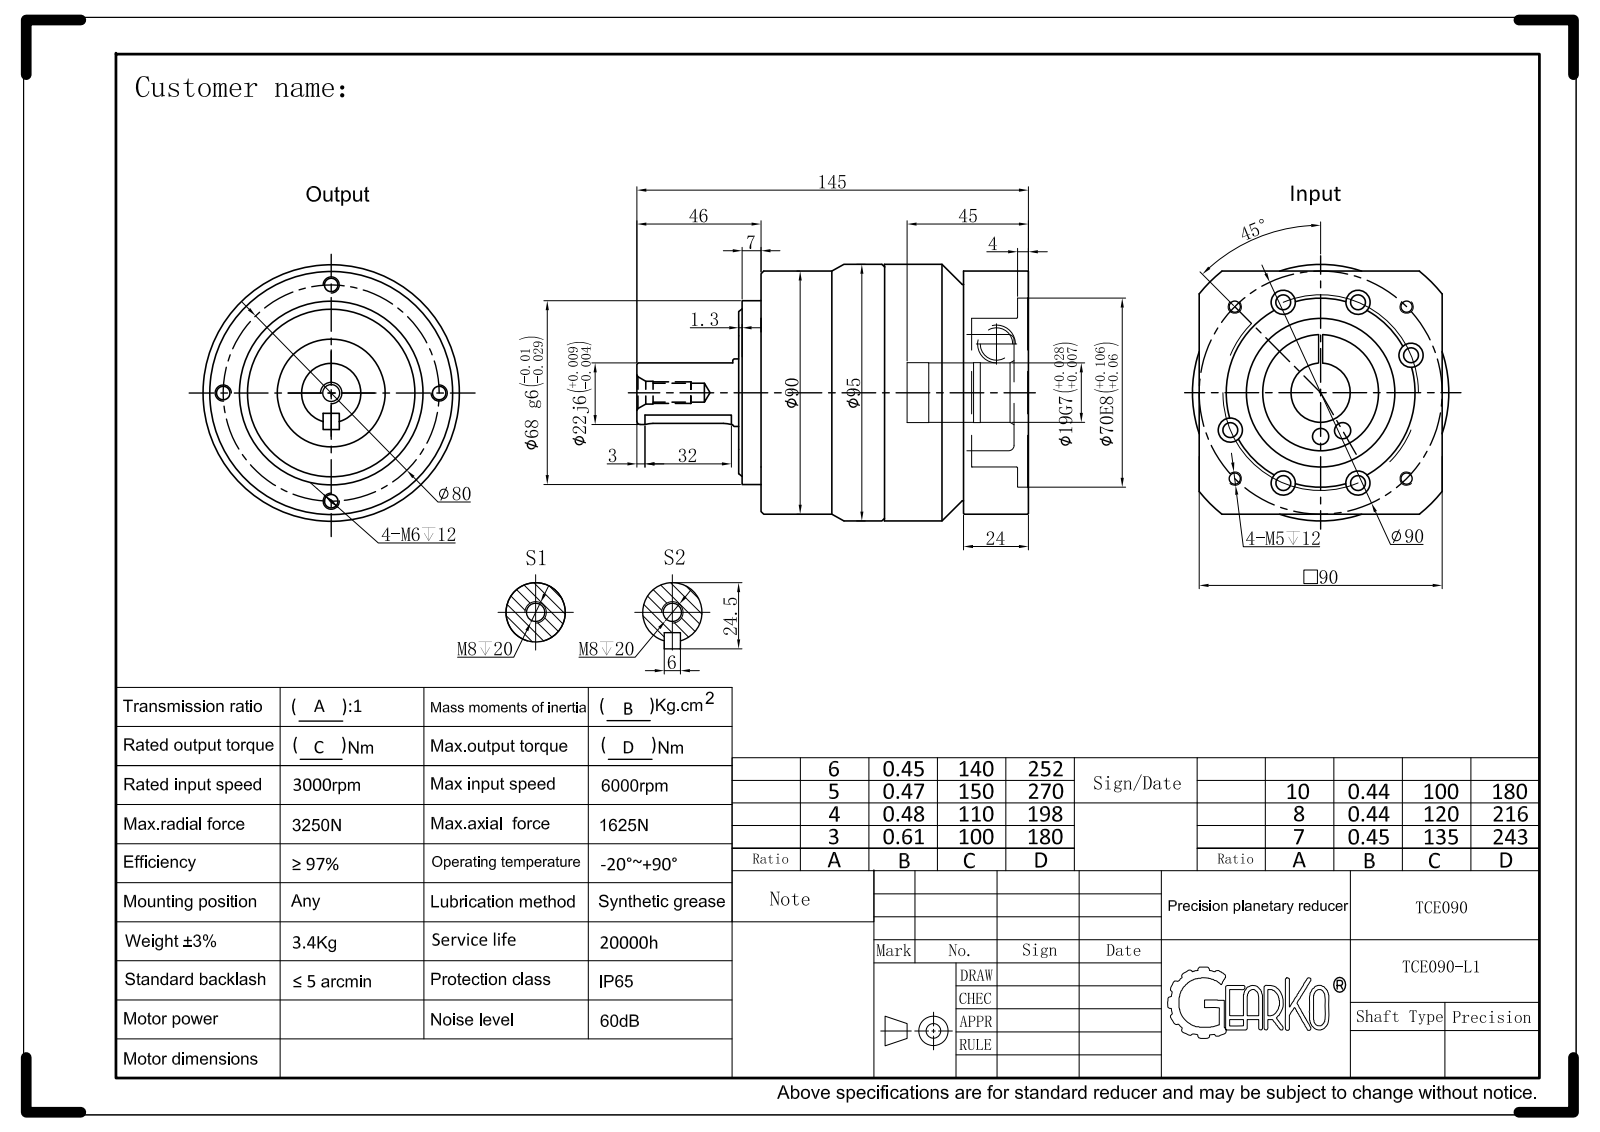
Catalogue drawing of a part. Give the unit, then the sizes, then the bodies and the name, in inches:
Units: inches
Overall size (bounding box): 5.709 × 3.74 × 3.74
Round holes (diameter × count): ⌀0.165 ×4, ⌀0.201 ×4, ⌀0.236 ×2, ⌀0.256 ×1, ⌀0.276 ×1, ⌀0.394 ×1, ⌀0.472 ×1, ⌀0.551 ×1, ⌀0.748 ×1, ⌀1.181 ×1, ⌀1.575 ×1, ⌀2.165 ×1
Round bosses / shafts (diameter × count): ⌀3.74 ×1, ⌀3.543 ×1, ⌀3.15 ×1, ⌀2.677 ×1, ⌀1.693 ×1, ⌀0.984 ×1, ⌀0.866 ×1
Partial cylindrical surfaces — rounded edges, fillets, slot ends (radius × count): R0.118 ×2, R2.28 ×1
Main face-to-face distances: 2.098, 2.126, 3.543, 0.327, 4.224, 1.799, 3.898, 0.945, 3.28, 2.953
Hole centre spacings: 1.293, 3.092, 1.575, 1.77, 2.227, 2.504, 1.393, 1.7
Volume: 41.7 in³ · Surface area: 136.1 in²
Bodies: 3 solids, 118 faces (41 planar, 39 cylindrical, 38 other)
Part name (STEP PRODUCT): model236
STEP written by: SIEMENS PLM Software NX 10.0 (CONFIG_CONTROL_DESIGN)
